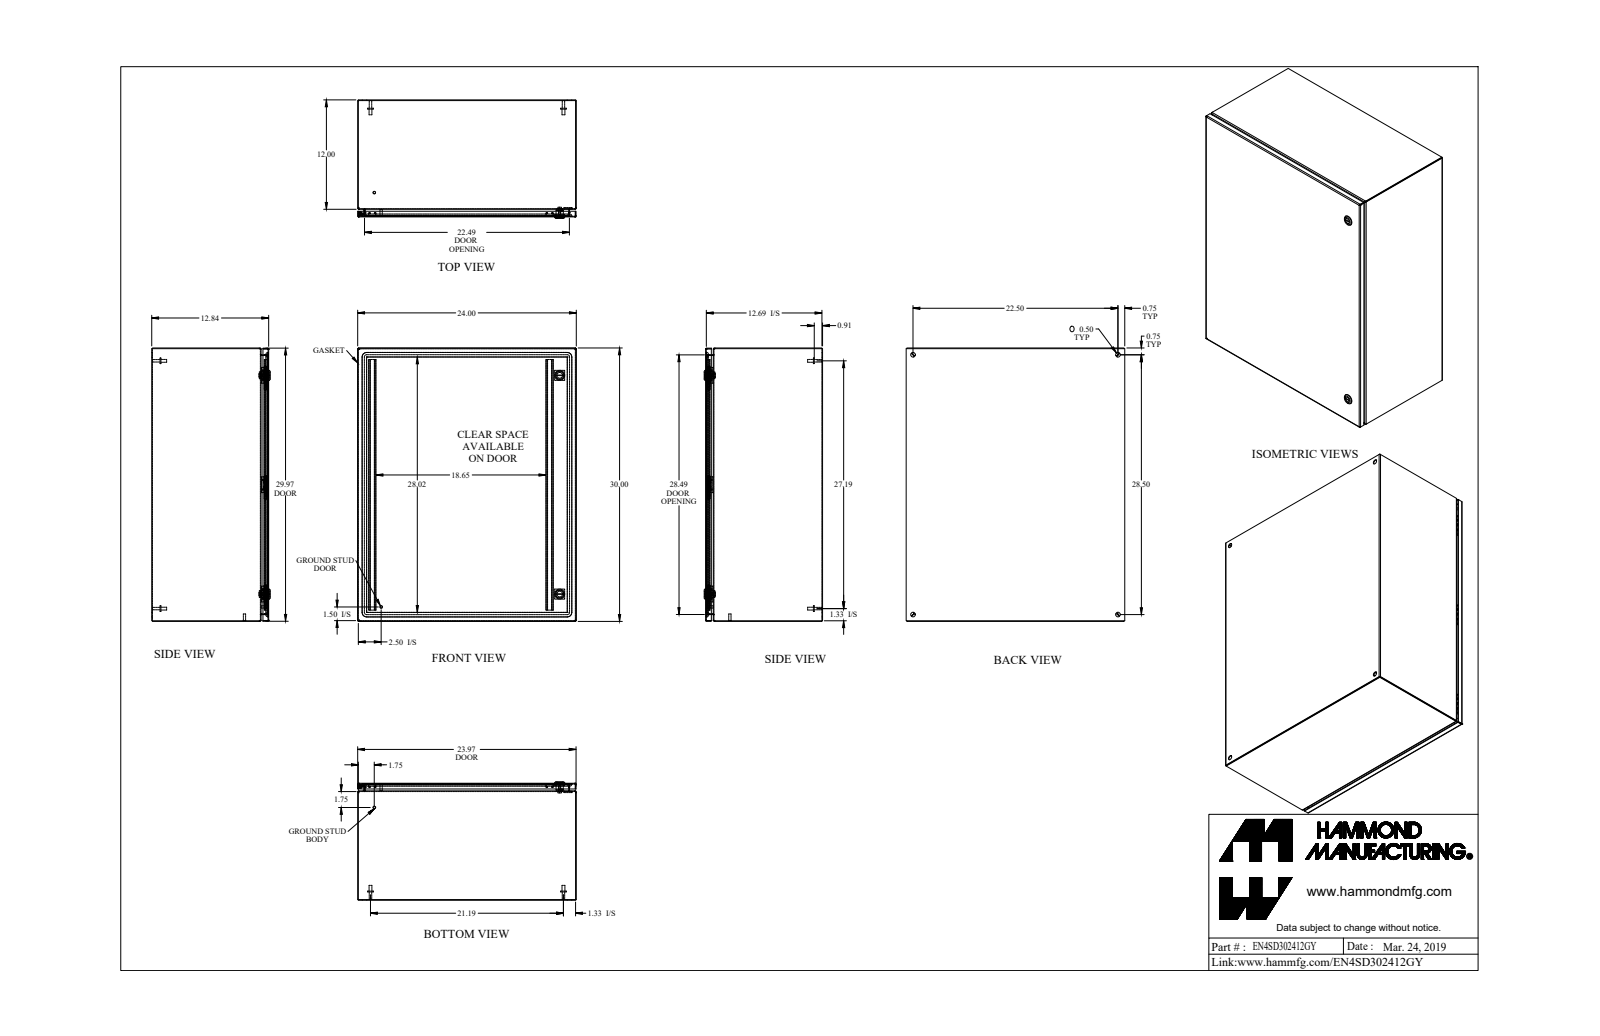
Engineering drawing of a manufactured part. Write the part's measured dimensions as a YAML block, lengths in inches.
part_name: "EN4SD302412GY"
step_written_by: "SolidWorks 2019 (AUTOMOTIVE_DESIGN)"
units: inches
bodies: {solids: 33, faces: 838, planar: 399, cylindrical: 283, other: 156}
overall_size: [30, 24, 12.997]
volume: 226.3
surface_area: 6351
round_holes:
  - {diameter: 0.5, count: 4}
  - {diameter: 0.232, count: 2}
  - {diameter: 0.625, count: 2}
  - {diameter: 0.785, count: 2}
  - {diameter: 0.172, count: 1}
  - {diameter: 0.24, count: 1}
  - {diameter: 0.242, count: 1}
round_bosses_or_shafts:
  - {diameter: 0.625, count: 4}
  - {diameter: 0.313, count: 4}
  - {diameter: 0.27, count: 4}
  - {diameter: 1.1, count: 2}
  - {diameter: 0.525, count: 2}
  - {diameter: 0.281, count: 2}
  - {diameter: 0.25, count: 2}
  - {diameter: 0.455, count: 1}
partial_cylinders:
  - {radius: 0.036, count: 14}
  - {radius: 0.108, count: 14}
  - {radius: 0.043, count: 12}
  - {radius: 0.081, count: 12}
  - {radius: 0.312, count: 12}
  - {radius: 0.1, count: 8}
  - {radius: 0.006, count: 6}
  - {radius: 0.062, count: 6}
face_to_face_distances: [0.072, 12.765, 12.693, 12.837, 23.928, 29.928, 23.856, 24, 29.856, 30]
hole_center_spacings: [22.5, 28.5, 36.311, 2.493, 2.494, 21.545, 21.545, 23.999]
